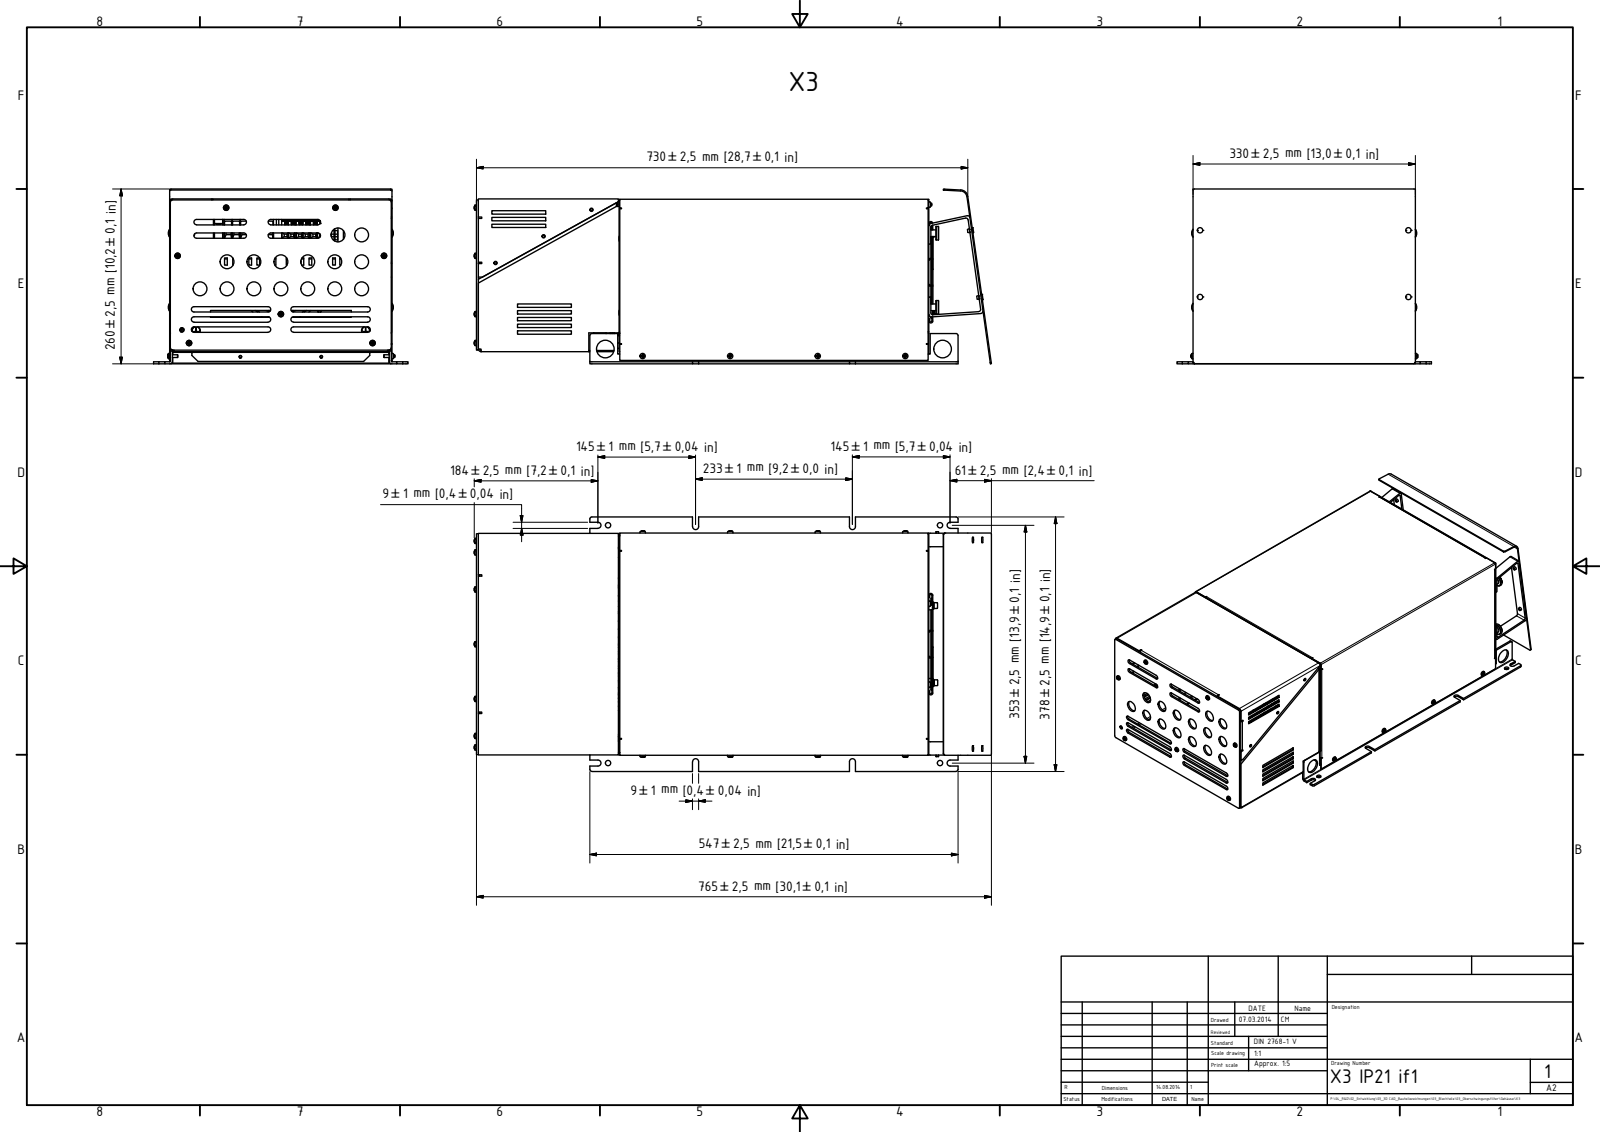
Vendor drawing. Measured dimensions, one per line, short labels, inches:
name: 10100256 Bodenblech X3; 10100388 Deckel RHF-BG X3-A; 10100387 Anschlussblech RHF-BG X3-A; 10100262 Lüfterblech RHF-BG X3-A (+8 more)
written by: Autodesk Inventor 2015 (AUTOMOTIVE_DESIGN)
unit: in
bodies: 111 solids, 8876 faces (5196 planar, 2478 cylindrical, 1202 other)
size: 30.234 × 14.882 × 10.217
volume: 143 in³; area: 4 176 in²
holes: 29× ⌀0.128, 23× ⌀0.197, 19× ⌀0.268, 15× ⌀0.807, 14× ⌀0.157, 12× ⌀0.249, 6× ⌀0.276, 6× ⌀0.315, 6× ⌀0.323, 6× ⌀0.374, 5× ⌀0.236, 5× ⌀0.256
bosses: 25× ⌀0.157, 11× ⌀0.144, 10× ⌀0.143, 8× ⌀0.055, 6× ⌀0.394, 6× ⌀0.315, 4× ⌀0.787, 4× ⌀0.63
rounds: 112× R0.009, 85× R0.02, 68× R0.039, 57× R0.006, 52× R0.079, 45× R0.004, 40× R0.157, 39× R0.004
face distances: 0.039, 0.079, 0.118, 12.953, 12.913, 18.071, 0.059, 8.854, 12.992, 8.839
hole spacings: 0.827, 12.185, 1.432, 4.724, 5.118, 0.469, 1.076, 1.969
